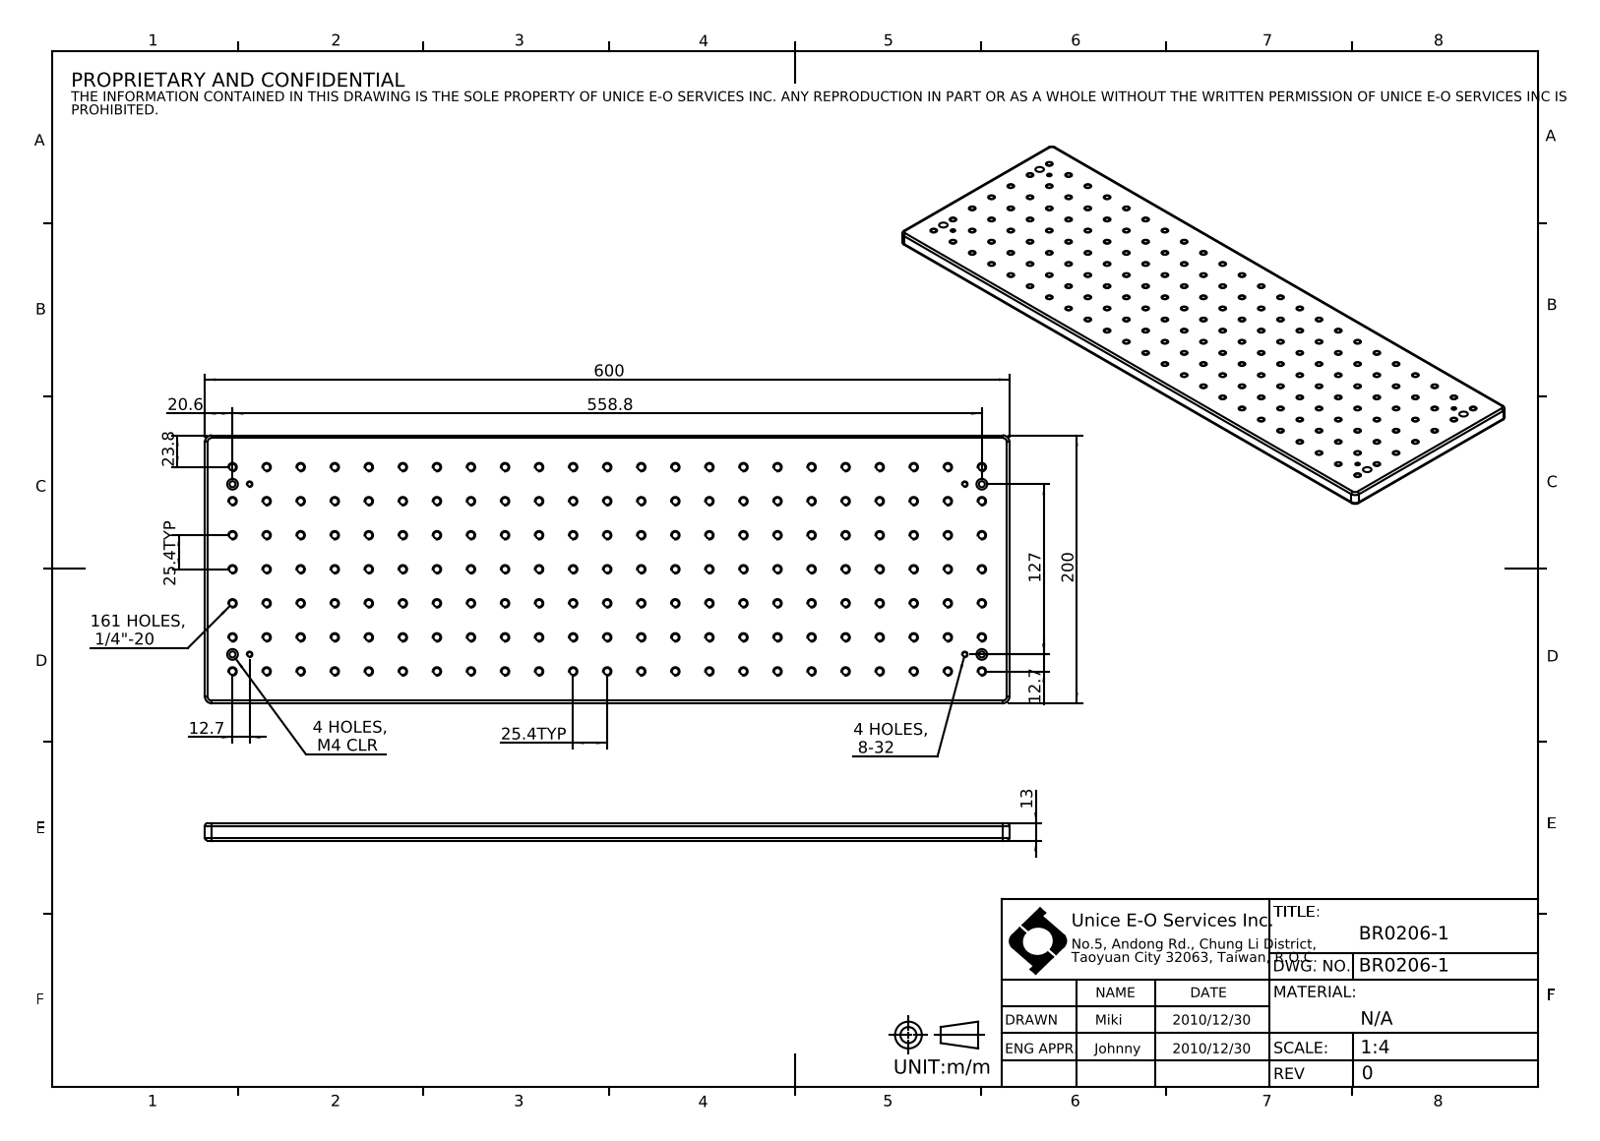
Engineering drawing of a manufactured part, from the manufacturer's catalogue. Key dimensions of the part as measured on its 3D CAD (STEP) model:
Part name (STEP PRODUCT): BR0206-1
STEP written by: SolidWorks 2016 (CONFIG_CONTROL_DESIGN)
Units: millimetres
Bodies: 1 solid, 376 faces (10 planar, 358 cylindrical, 8 other)
Overall size (bounding box): 600 × 200 × 13
Volume: 1 512 000 mm³ · Surface area: 286 249 mm²
Round holes (diameter × count): ⌀5.11 ×161, ⌀3.45 ×4, ⌀4.5 ×4, ⌀8 ×4
Partial cylindrical surfaces — rounded edges, fillets, slot ends (radius × count): R2 ×8, R5 ×4
Main face-to-face distances: 13, 200, 600, 7, 6
Hole centre spacings: 25.4, 50.8, 127, 154.5, 76.2, 160.64, 152.4, 170.39
